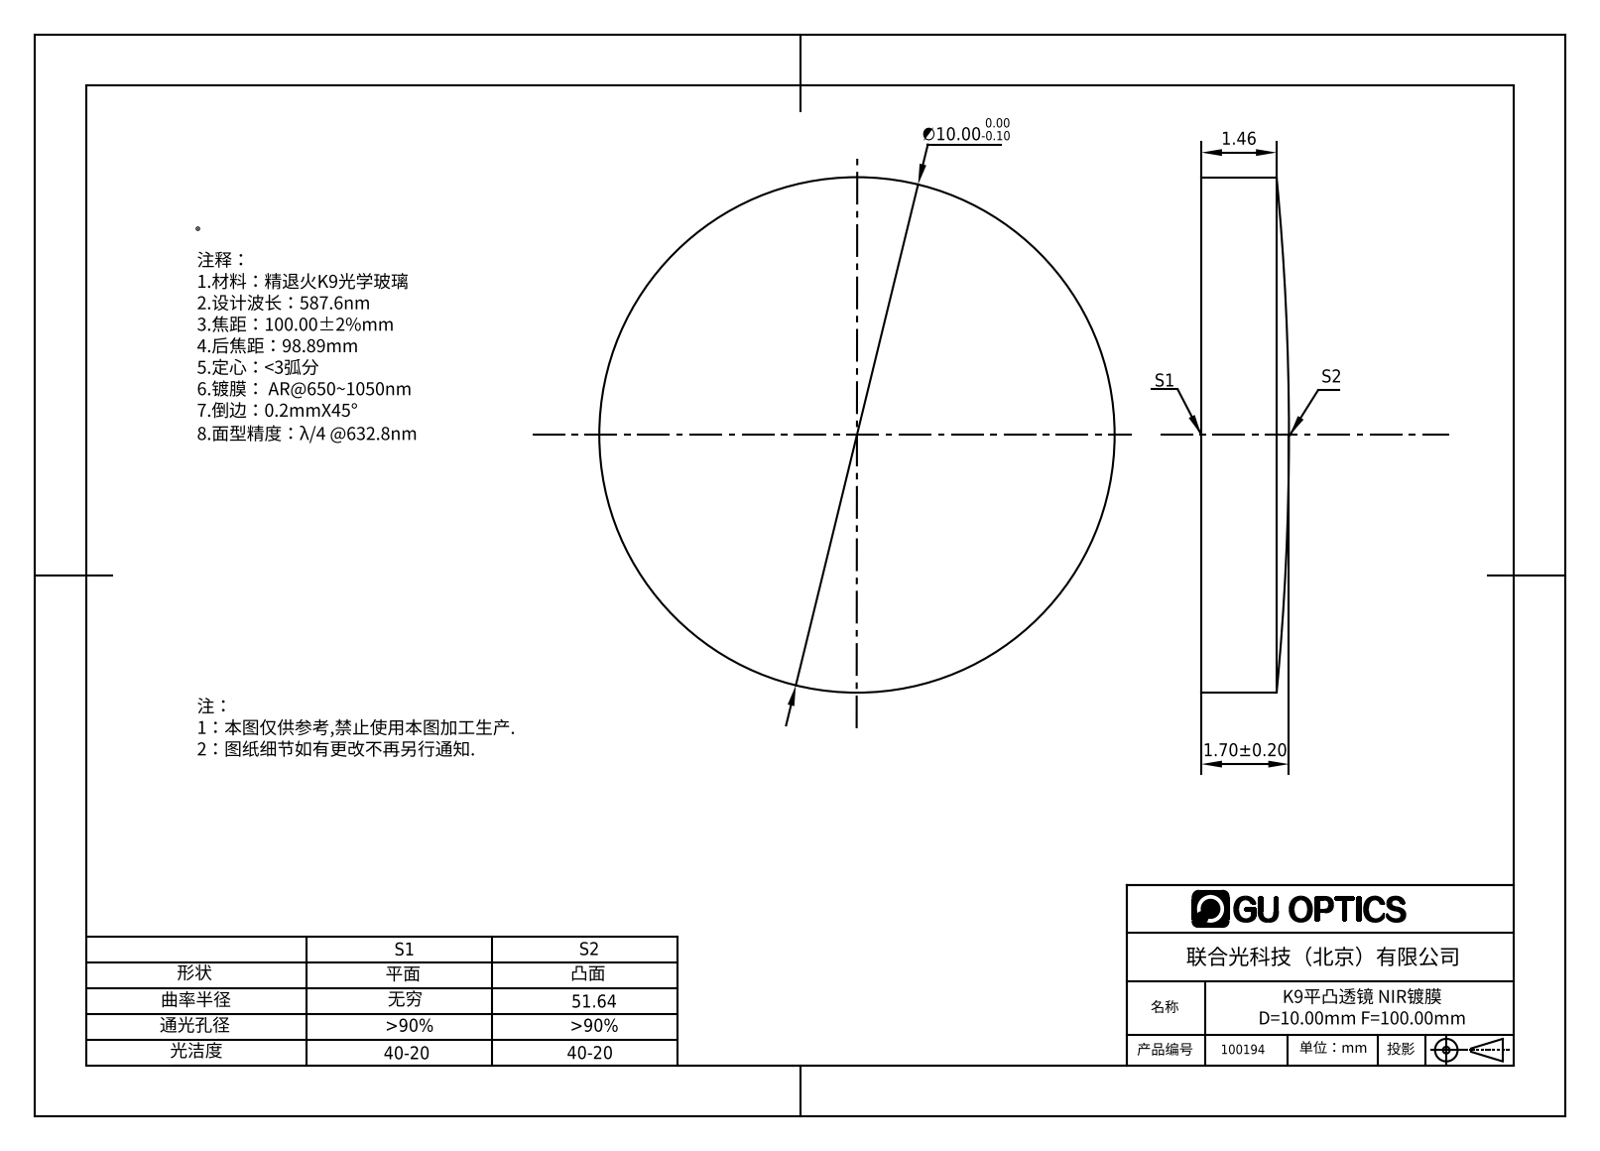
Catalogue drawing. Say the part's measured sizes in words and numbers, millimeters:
The part is named "100194". Its 3-D file was written by "SolidWorks 2016 (AUTOMOTIVE_DESIGN)". It is 1 solid with 5 faces: 1 planar, 2 cylindrical and 2 other. Overall it measures 10 by 10 by 1.7 millimeters. Its volume is 124 cubic millimeters and its surface area 203 square millimeters. Round bosses or shafts: 1 of diameter 10.
